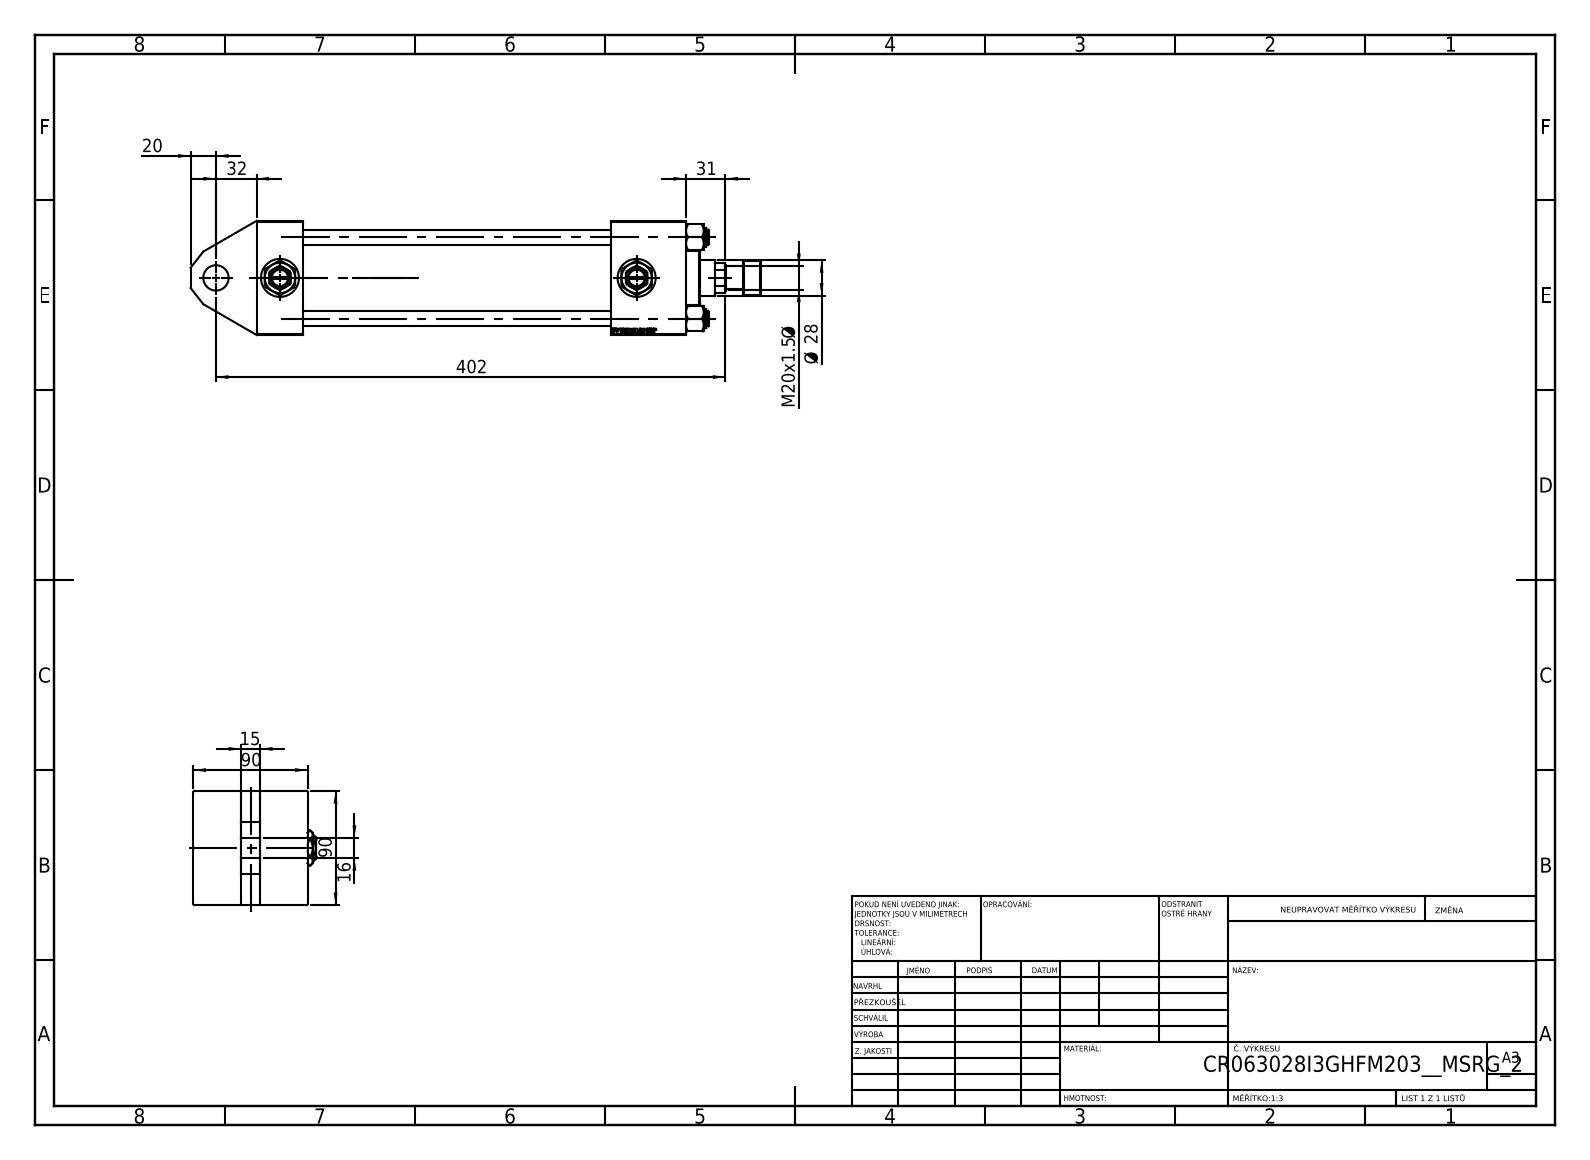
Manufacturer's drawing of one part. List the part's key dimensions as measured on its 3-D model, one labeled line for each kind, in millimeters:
Part name (STEP PRODUCT): V215CR_VCP_I; V215_VC_A; V215CR_TYCINKA_I; NUT_M5_I (+3 more)
STEP written by: SolidWorks 2019 (CONFIG_CONTROL_DESIGN)
Units: millimetres
Bodies: 14 solids, 1194 faces (554 planar, 96 cylindrical, 544 other)
Overall size (bounding box): 450 × 97 × 90
Volume: 1 315 000 mm³ · Surface area: 317 773 mm²
Round holes (diameter × count): ⌀12 ×4, ⌀7 ×2, ⌀20.96 ×2, ⌀30 ×2, ⌀18.5 ×1, ⌀20 ×1, ⌀28 ×1, ⌀31 ×1, ⌀50 ×1, ⌀60 ×1, ⌀63 ×1
Round bosses / shafts (diameter × count): ⌀15 ×4, ⌀69 ×1, ⌀42 ×1, ⌀27 ×1, ⌀18 ×1
Main face-to-face distances: 90, 37, 339, 302, 59, 37.5, 52.5, 280, 243, 310.3
Hole centre spacings: 45.47, 64.3, 90.93, 50.5, 281.5, 332
